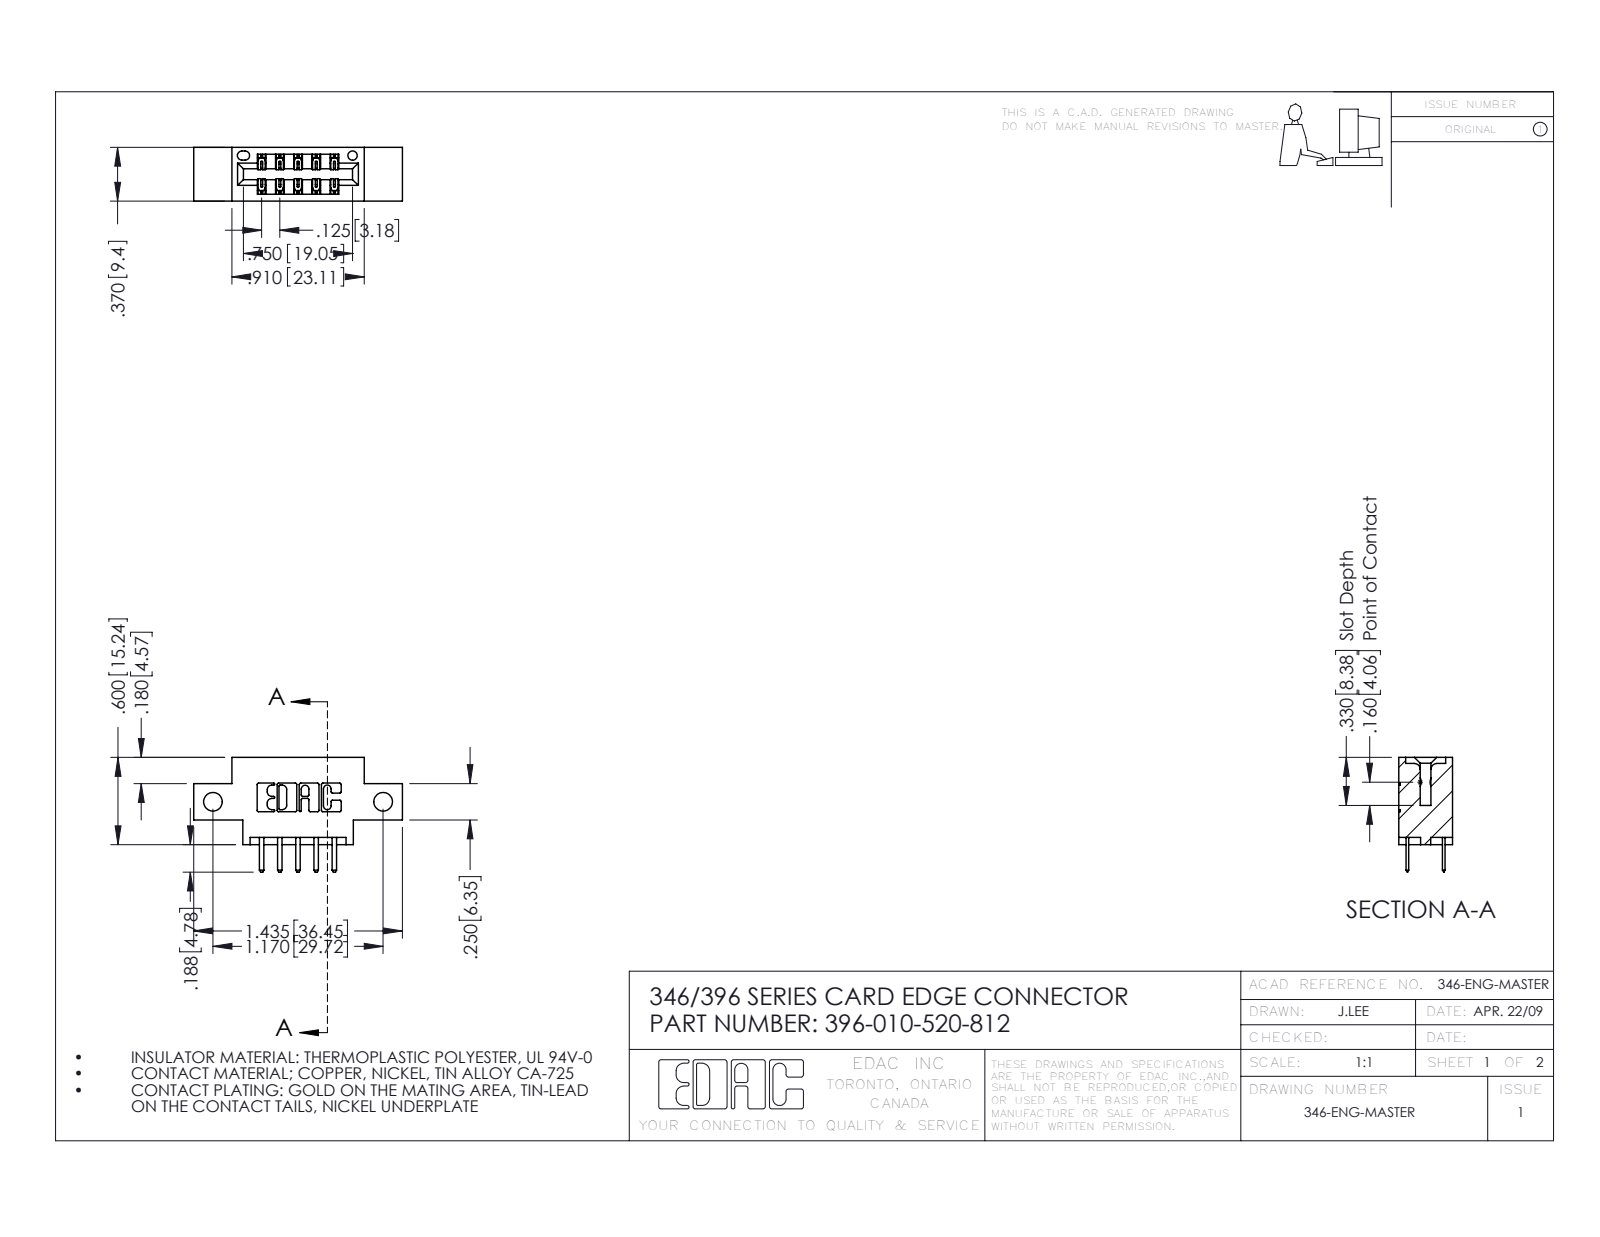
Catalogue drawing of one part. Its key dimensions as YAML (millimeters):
part_name: "396-010-520-812; 345-292-001_345-293-120; 346 Part_0.170 Offset - Side Mount"
step_written_by: "SolidWorks 2016 (CONFIG_CONTROL_DESIGN)"
units: millimeters
bodies: {solids: 11, faces: 686, planar: 450, cylindrical: 236, other: 0}
overall_size: [36.4, 20, 9.4]
volume: 3020
surface_area: 3603
round_holes:
  - {diameter: 3.3, count: 2}
  - {diameter: 1.6, count: 1}
partial_cylinders:
  - {radius: 0.3, count: 22}
  - {radius: 0.2, count: 15}
  - {radius: 0.3, count: 14}
  - {radius: 0.2, count: 6}
  - {radius: 0.8, count: 6}
  - {radius: 0.7, count: 3}
  - {radius: 0.4, count: 2}
  - {radius: 0.6, count: 2}
face_to_face_distances: [6.4, 9.4, 1.2, 8.2, 3.8, 5.6, 2.5, 4.4, 14, 1.8]
hole_center_spacings: [29.7]
